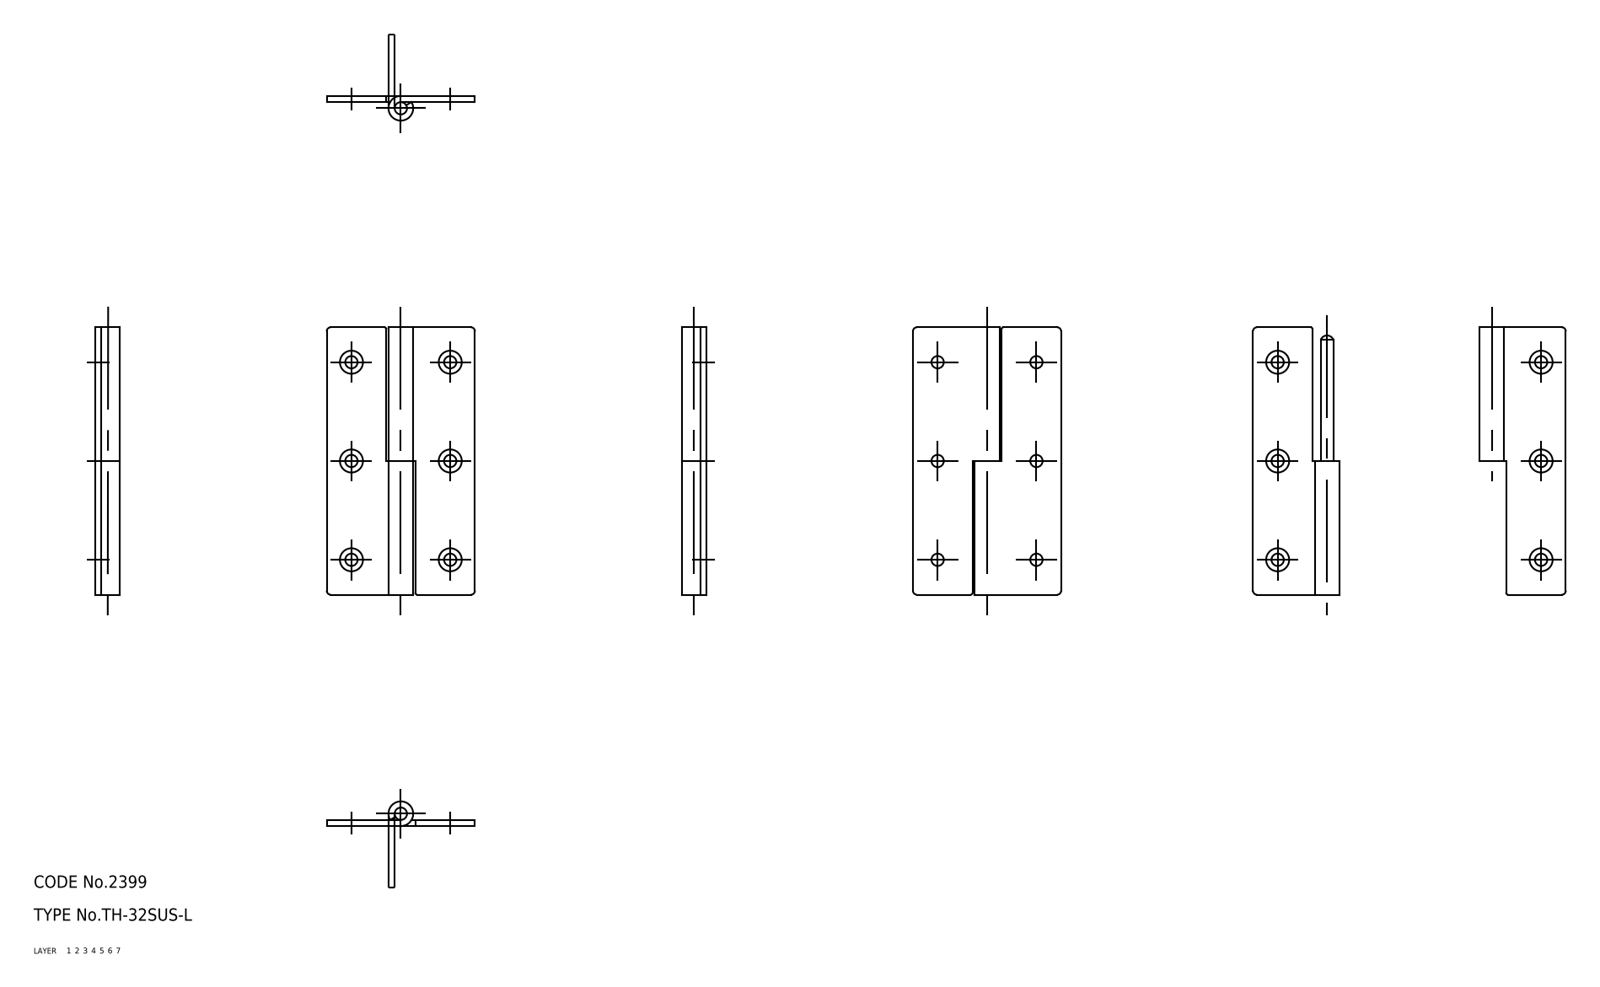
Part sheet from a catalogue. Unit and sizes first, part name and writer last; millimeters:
Units: millimetres
Overall size (bounding box): 65 × 36 × 6
Volume: 4 630 mm³ · Surface area: 6 887 mm²
Bodies: 3 solids, 54 faces (0 planar, 0 cylindrical, 54 other)
Part name (STEP PRODUCT): shaft; hinge piece_B; hinge piece_A; TH_32SUS_L_7958_36
STEP written by: CADfix (AUTOMOTIVE_DESIGN)
